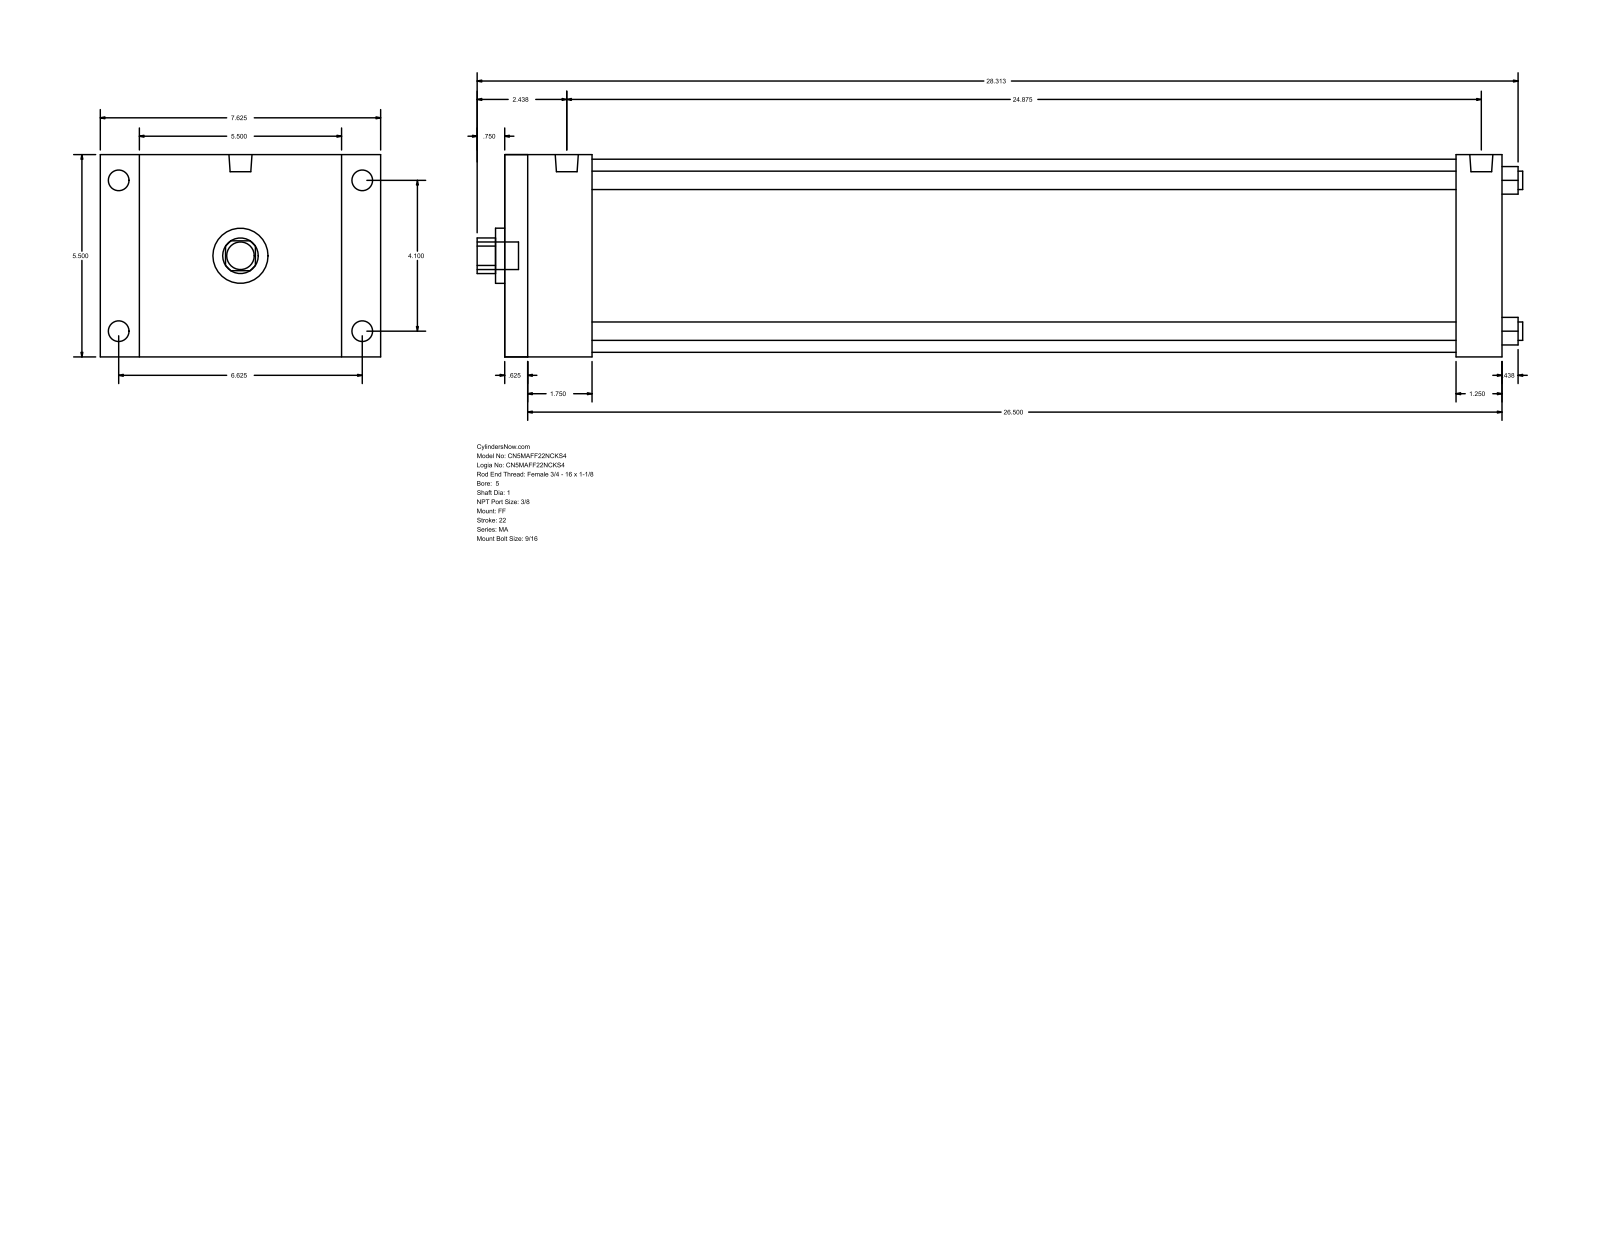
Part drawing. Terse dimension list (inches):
name: MA_FF__0500_1
written by: GSSL Pune (CONFIG_CONTROL_DESIGN)
unit: in
bodies: 0 solids, 92 faces (64 planar, 28 cylindrical, 0 other)
size: 28.437 × 7.625 × 5.5
holes: 4× ⌀0.5, 1× ⌀1, 1× ⌀1.5, 1× ⌀5.25
bosses: 4× ⌀0.563, 4× ⌀0.437, 2× ⌀0.627, 1× ⌀0.75
rounds: 1× R0.484
face distances: 5.5, 27.125, 0.625, 26.5, 25.875, 25.25, 1.25, 2.375, 1.75, 23.5
hole spacings: 2.899, 4.1, 5.798
